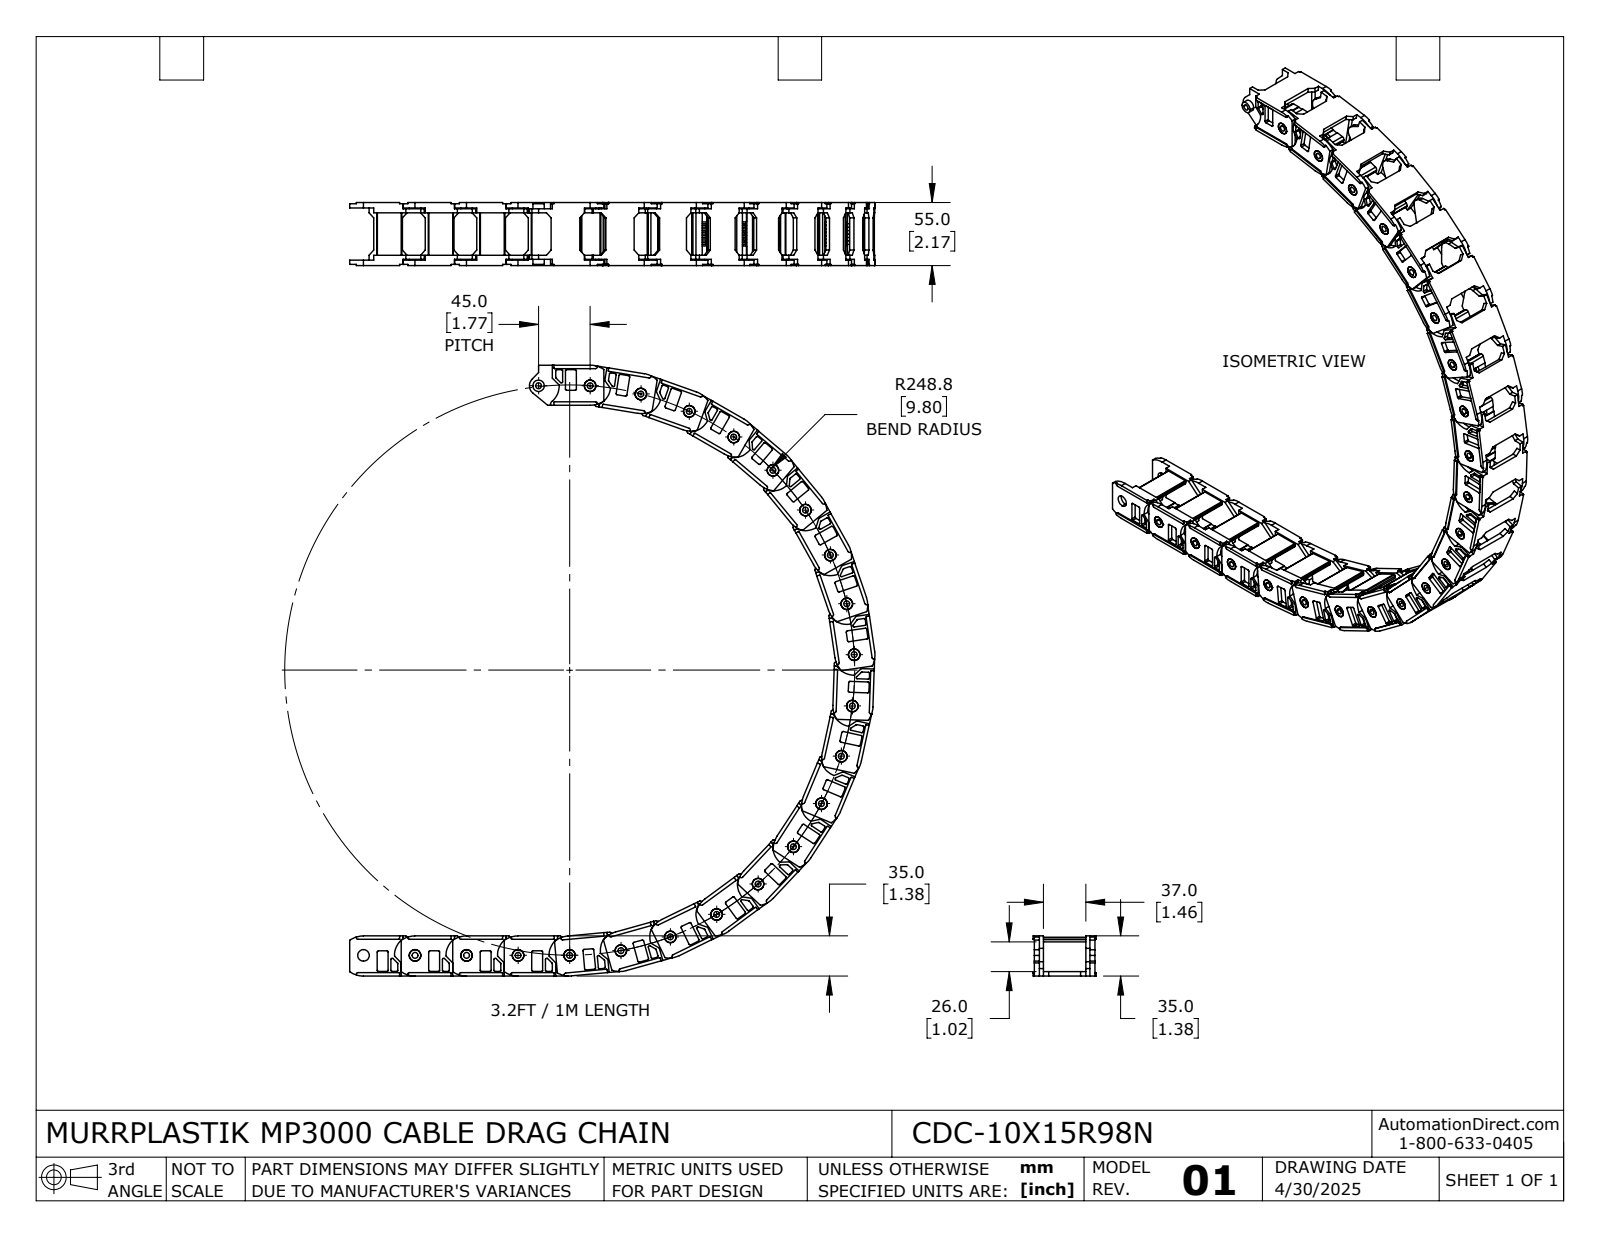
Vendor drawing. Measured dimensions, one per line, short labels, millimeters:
name: CDC-10X15R98N
written by: SolidWorks 2024 (AUTOMOTIVE_DESIGN)
unit: mm
bodies: 22 solids, 3696 faces (2596 planar, 1100 cylindrical, 0 other)
size: 533.12 × 458.53 × 55
volume: 587 391 mm³; area: 349 280 mm²
holes: 22× ⌀5.1, 22× ⌀10.1
bosses: 22× ⌀10
rounds: 176× R1, 88× R0.5, 44× R1.5, 44× R2, 44× R21, 22× R2.8, 22× R8, 22× R18
face distances: 45, 8, 4, 3.7, 49.3, 4.3, 41.3, 37, 3.5, 0.8
hole spacings: 45, 44.86, 89.36, 89.5, 44.87, 89.24, 133.12, 133.17
